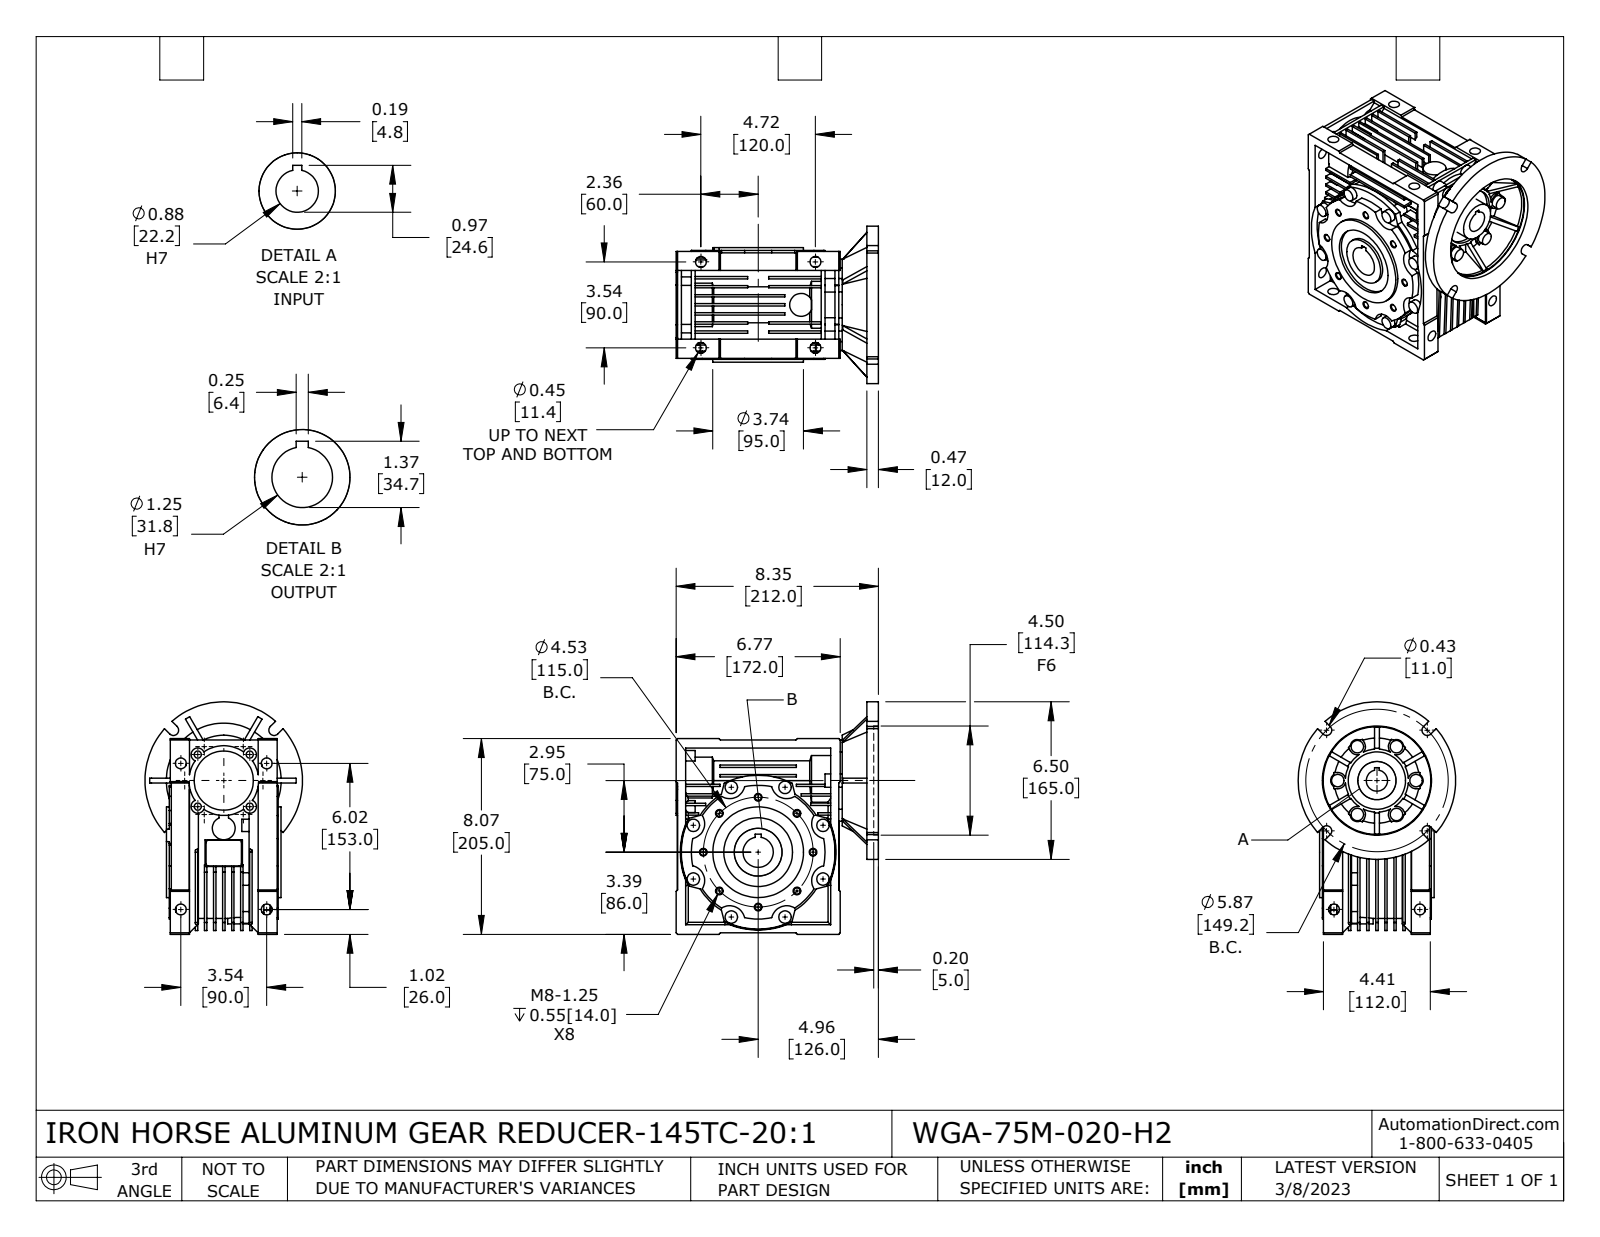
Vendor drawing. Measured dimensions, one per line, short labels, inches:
name: WGA-75M-020-H2
written by: SolidWorks 2021 (CONFIG_CONTROL_DESIGN)
unit: in
bodies: 4 solids, 1179 faces (675 planar, 386 cylindrical, 118 other)
size: 9.587 × 8.346 × 6.496
volume: 180 in³; area: 782.1 in²
holes: 8× ⌀0.262, 8× ⌀0.448, 4× ⌀0.293, 1× ⌀0.875, 1× ⌀0.906, 1× ⌀1, 1× ⌀1.25, 1× ⌀1.535, 1× ⌀1.654, 1× ⌀1.969, 1× ⌀2.441, 1× ⌀2.677
bosses: 14× ⌀0.512, 3× ⌀0.945, 1× ⌀6.496, 1× ⌀5.509, 1× ⌀5.465, 1× ⌀3.74, 1× ⌀2.992, 1× ⌀2.795
rounds: 10× R0.276, 8× R0.63, 6× R0.295, 6× R0.335, 4× R0.098, 4× R0.217, 1× R1.299, 1× R1.417
face distances: 0.374, 0.098, 0.472, 0.748, 0.276, 1.122, 1.496, 0.394, 0.65, 0.846
hole spacings: 2.264, 1.733, 3.202, 4.183, 1.515, 2.143, 3.543, 4.528
